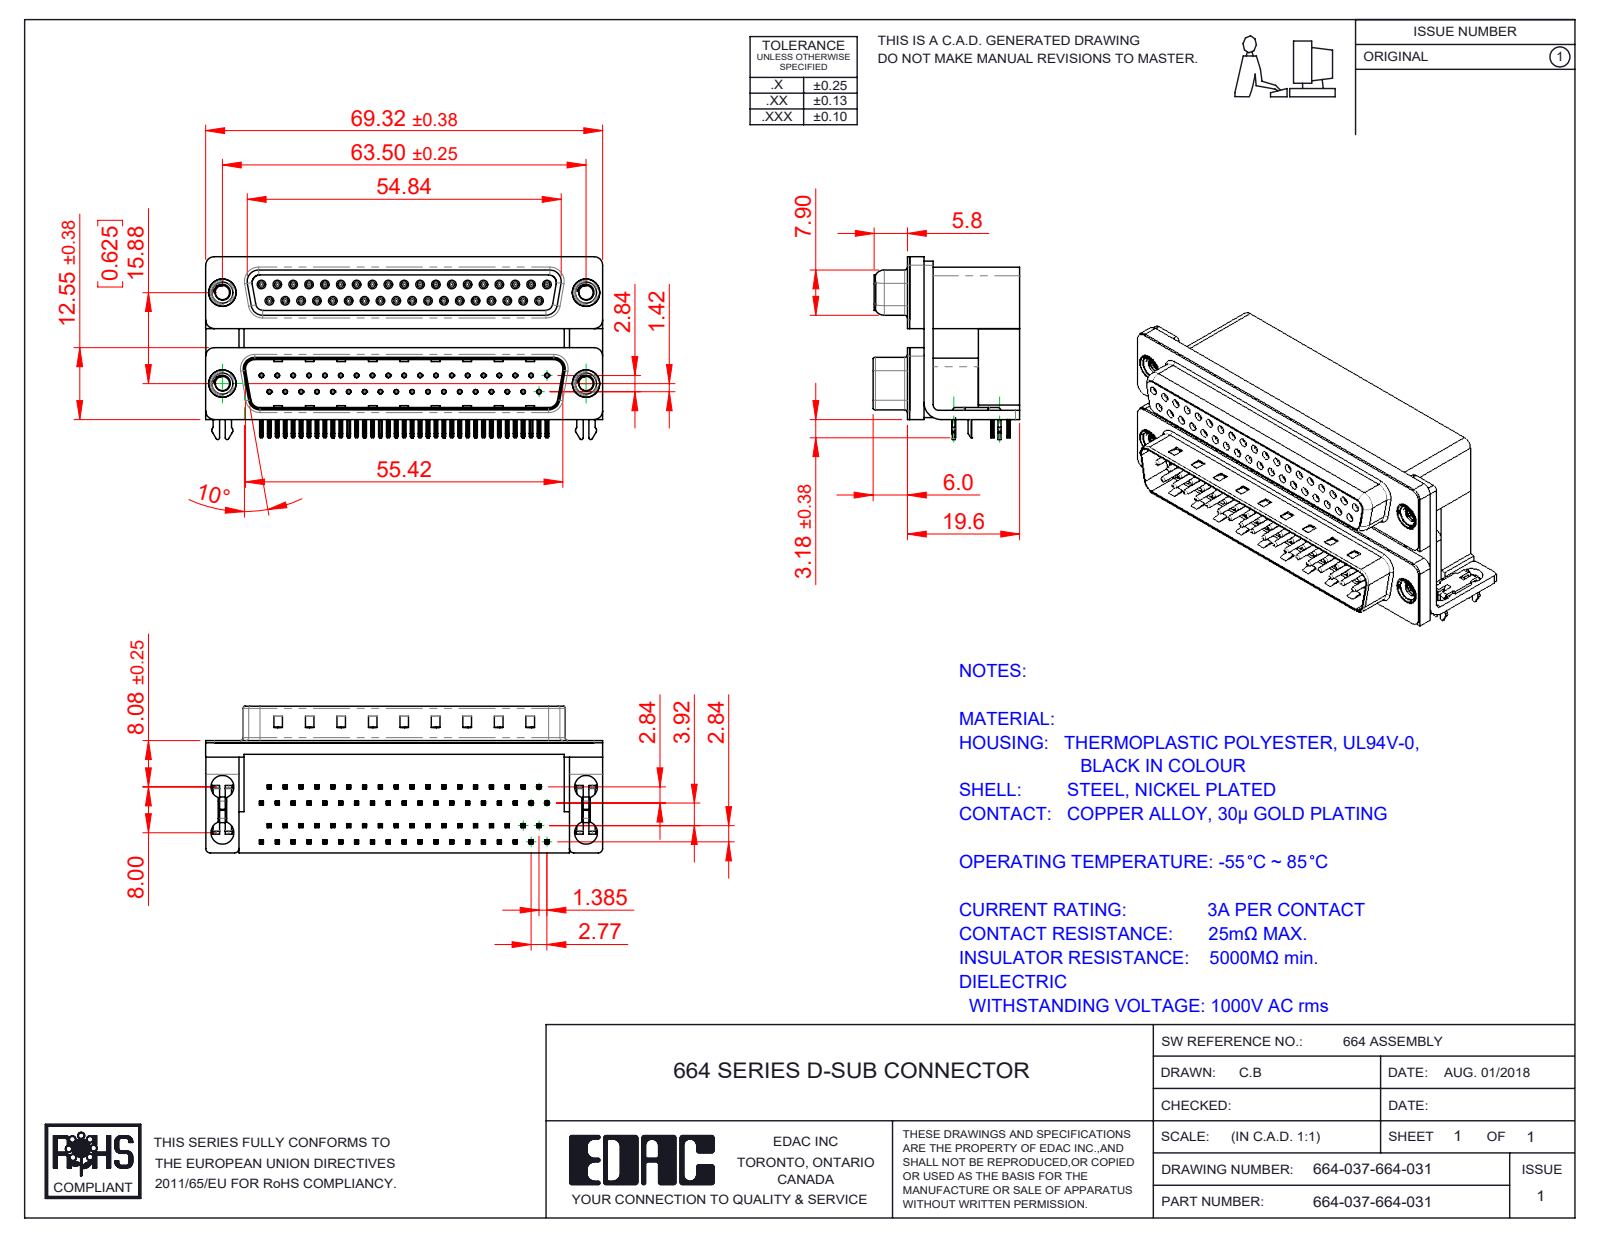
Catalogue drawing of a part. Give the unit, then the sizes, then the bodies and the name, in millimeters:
Units: millimetres
Overall size (bounding box): 69.32 × 31.93 × 25.6
Round holes (diameter × count): ⌀0.8 ×74, ⌀0.35 ×37, ⌀0.9 ×37, ⌀4 ×8, ⌀2.5 ×4, ⌀3.5 ×4, ⌀4.8 ×4, ⌀5 ×4
Round bosses / shafts (diameter × count): ⌀1.2 ×37, ⌀0.75 ×37, ⌀4.9 ×4, ⌀4.75 ×4, ⌀3.9 ×4
Partial cylindrical surfaces — rounded edges, fillets, slot ends (radius × count): R0.1 ×298, R0.25 ×158, R0.15 ×148, R0.12 ×74, R0.35 ×74, R0.34 ×37, R0.28 ×18, R0.5 ×16
Main face-to-face distances: 0.4, 19.2, 7.2, 12, 2.19, 15.52, 2.84, 26.22, 10.7, 13.33
Hole centre spacings: 2.77, 5.54, 3.16, 8.31, 11.08, 13.85, 16.62, 19.39
Volume: 29 789 mm³ · Surface area: 31 702 mm²
Bodies: 87 solids, 9101 faces (4843 planar, 2235 cylindrical, 2023 other)
Part name (STEP PRODUCT): 664 Contact Bottom Upper_L; 664 2 Prong Board Lock_3; 664 Housing Lower_37 Contacts; 664 Mounting Bracket_2ProngL (+8 more)
STEP written by: SolidWorks 2020 (CONFIG_CONTROL_DESIGN)
